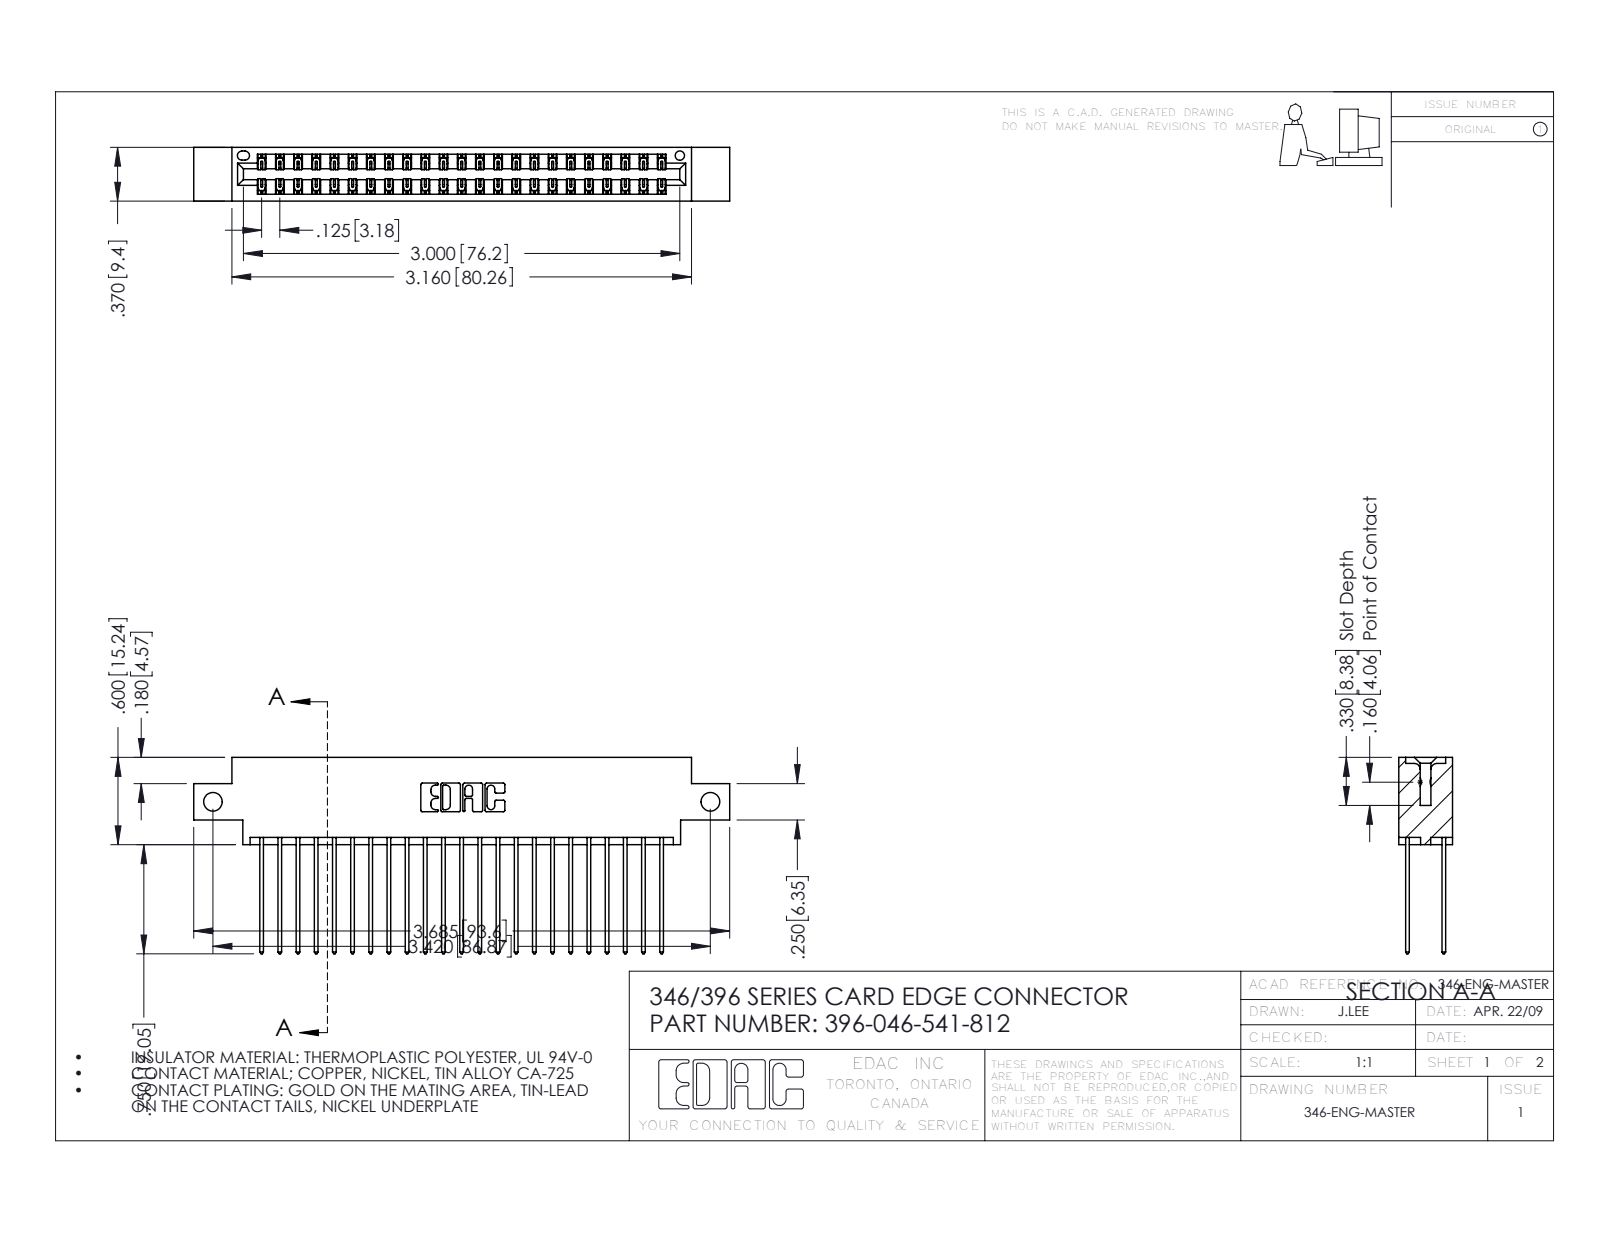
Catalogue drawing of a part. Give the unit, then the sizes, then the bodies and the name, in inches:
Units: inches
Overall size (bounding box): 3.685 × 1.35 × 0.37
Round holes (diameter × count): ⌀0.128 ×2, ⌀0.064 ×1
Partial cylindrical surfaces — rounded edges, fillets, slot ends (radius × count): R0.006 ×69, R0.01 ×46, R0.01 ×22, R0.007 ×6, R0.031 ×6, R0.026 ×3, R0.014 ×2, R0.022 ×2
Main face-to-face distances: 0.048, 0.322, 0.25, 0.072, 0.298, 0.025, 0.37, 0.275, 0.225, 0.148
Hole centre spacings: 3.42
Volume: 0.549 in³ · Surface area: 20.74 in²
Bodies: 47 solids, 2518 faces (1690 planar, 828 cylindrical, 0 other)
Part name (STEP PRODUCT): 345-292-001_345-293-141; 396-046-541-812; 346 Part_0.170 Offset - Side Mount
STEP written by: SolidWorks 2016 (CONFIG_CONTROL_DESIGN)
